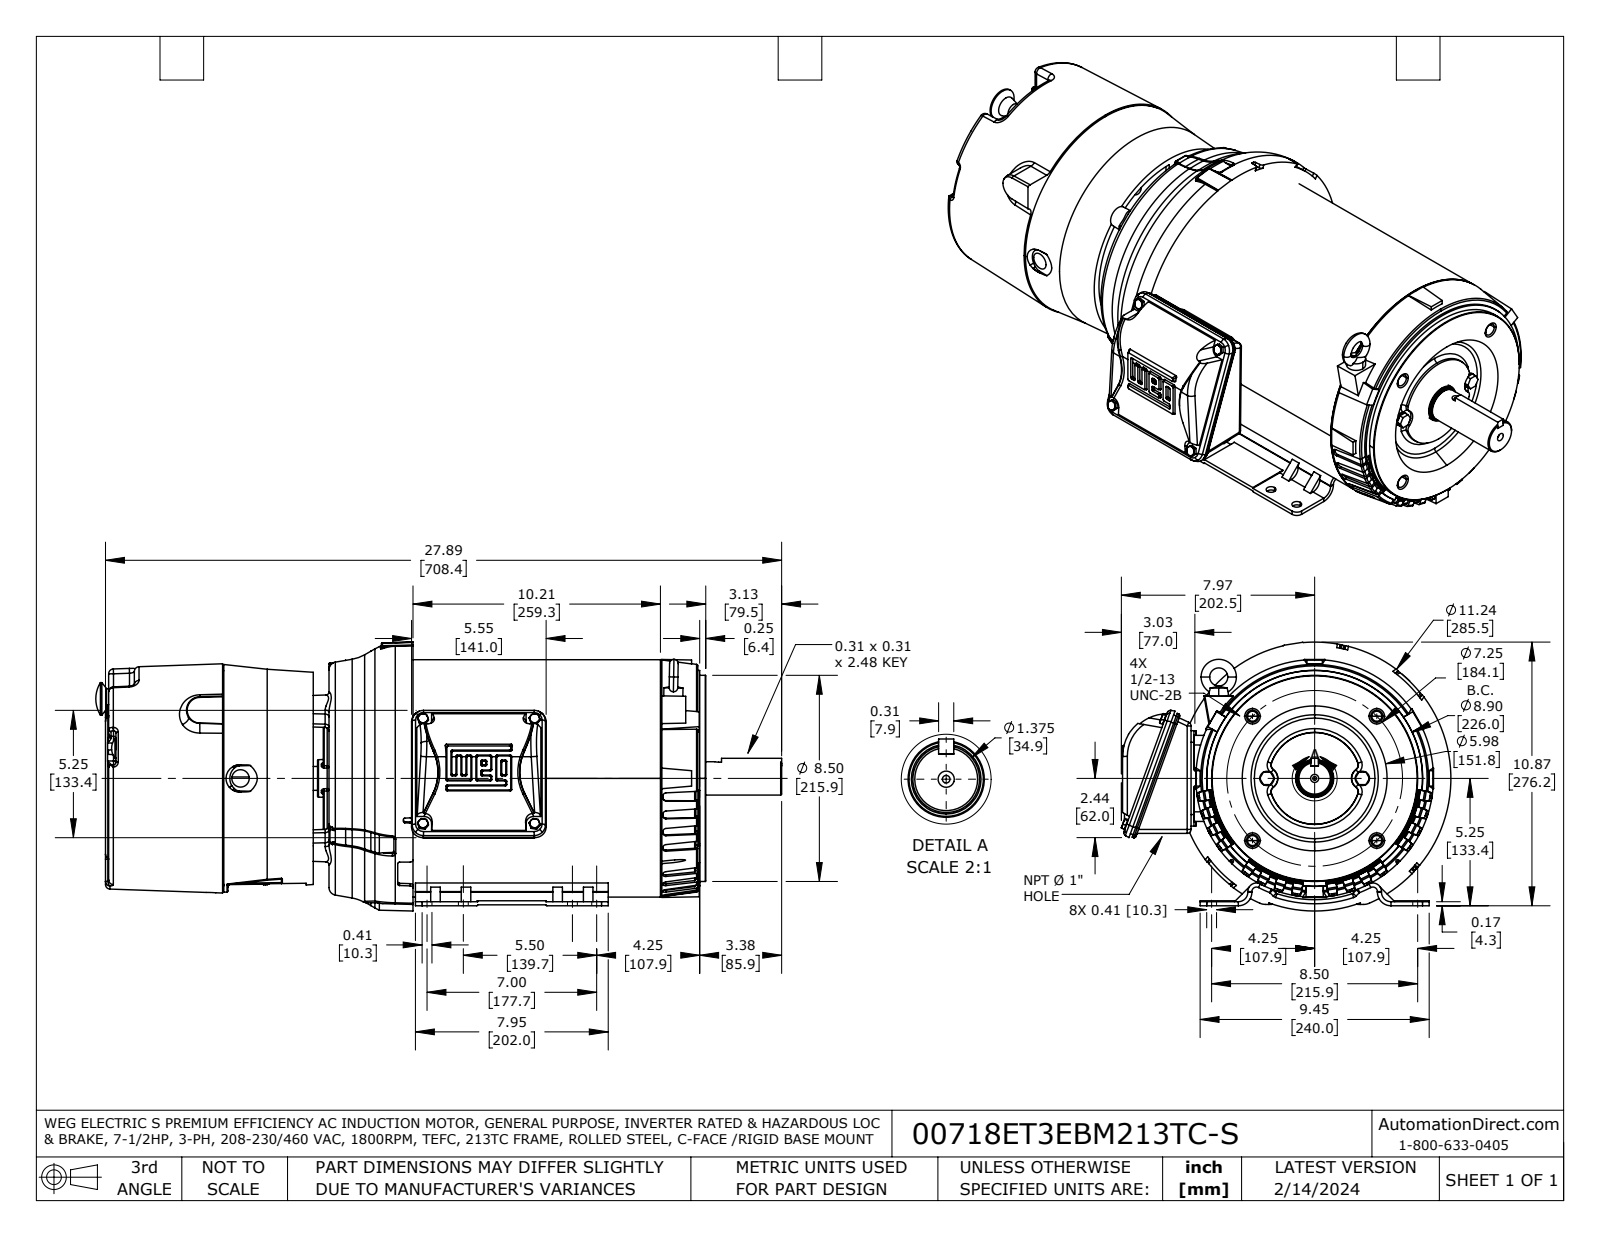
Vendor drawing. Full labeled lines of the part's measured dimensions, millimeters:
Part name (STEP PRODUCT): 13733398 nc ext1b BM n Bell n Shft 1a W std mtr wo bell shft 1b fxt b
STEP written by: SolidWorks 2021 (AUTOMOTIVE_DESIGN)
Units: millimetres
Bodies: 29 solids, 3384 faces (1166 planar, 678 cylindrical, 1540 other)
Overall size (bounding box): 718.6 × 345.3 × 281.6
Volume: 25 100 000 mm³ · Surface area: 1 564 000 mm²
Round holes (diameter × count): ⌀10.3 ×8, ⌀6.5 ×6, ⌀12.7 ×5, ⌀2.6 ×4, ⌀3.7 ×4, ⌀10.5 ×4, ⌀10.7 ×4, ⌀5.1 ×3, ⌀13.5 ×3, ⌀14.4 ×3, ⌀21.4 ×3, ⌀26.2 ×3
Round bosses / shafts (diameter × count): ⌀9 ×4, ⌀2.8 ×4, ⌀20.6 ×3, ⌀12.7 ×3, ⌀15 ×2, ⌀11.6 ×2, ⌀248.6 ×1, ⌀238.3 ×1
Partial cylindrical surfaces — rounded edges, fillets, slot ends (radius × count): R1.5 ×58, R3.2 ×32, R2.5 ×29, R2 ×24, R3 ×24, R1.3 ×23, R5.1 ×22, R1 ×19
Main face-to-face distances: 259.3, 10.7, 270, 70.6, 81.4, 340.6, 232.7, 303.3, 314, 573.3
Hole centre spacings: 101.6, 38.1, 46.2, 56.2, 66.8, 66.8, 67.7, 92.1
